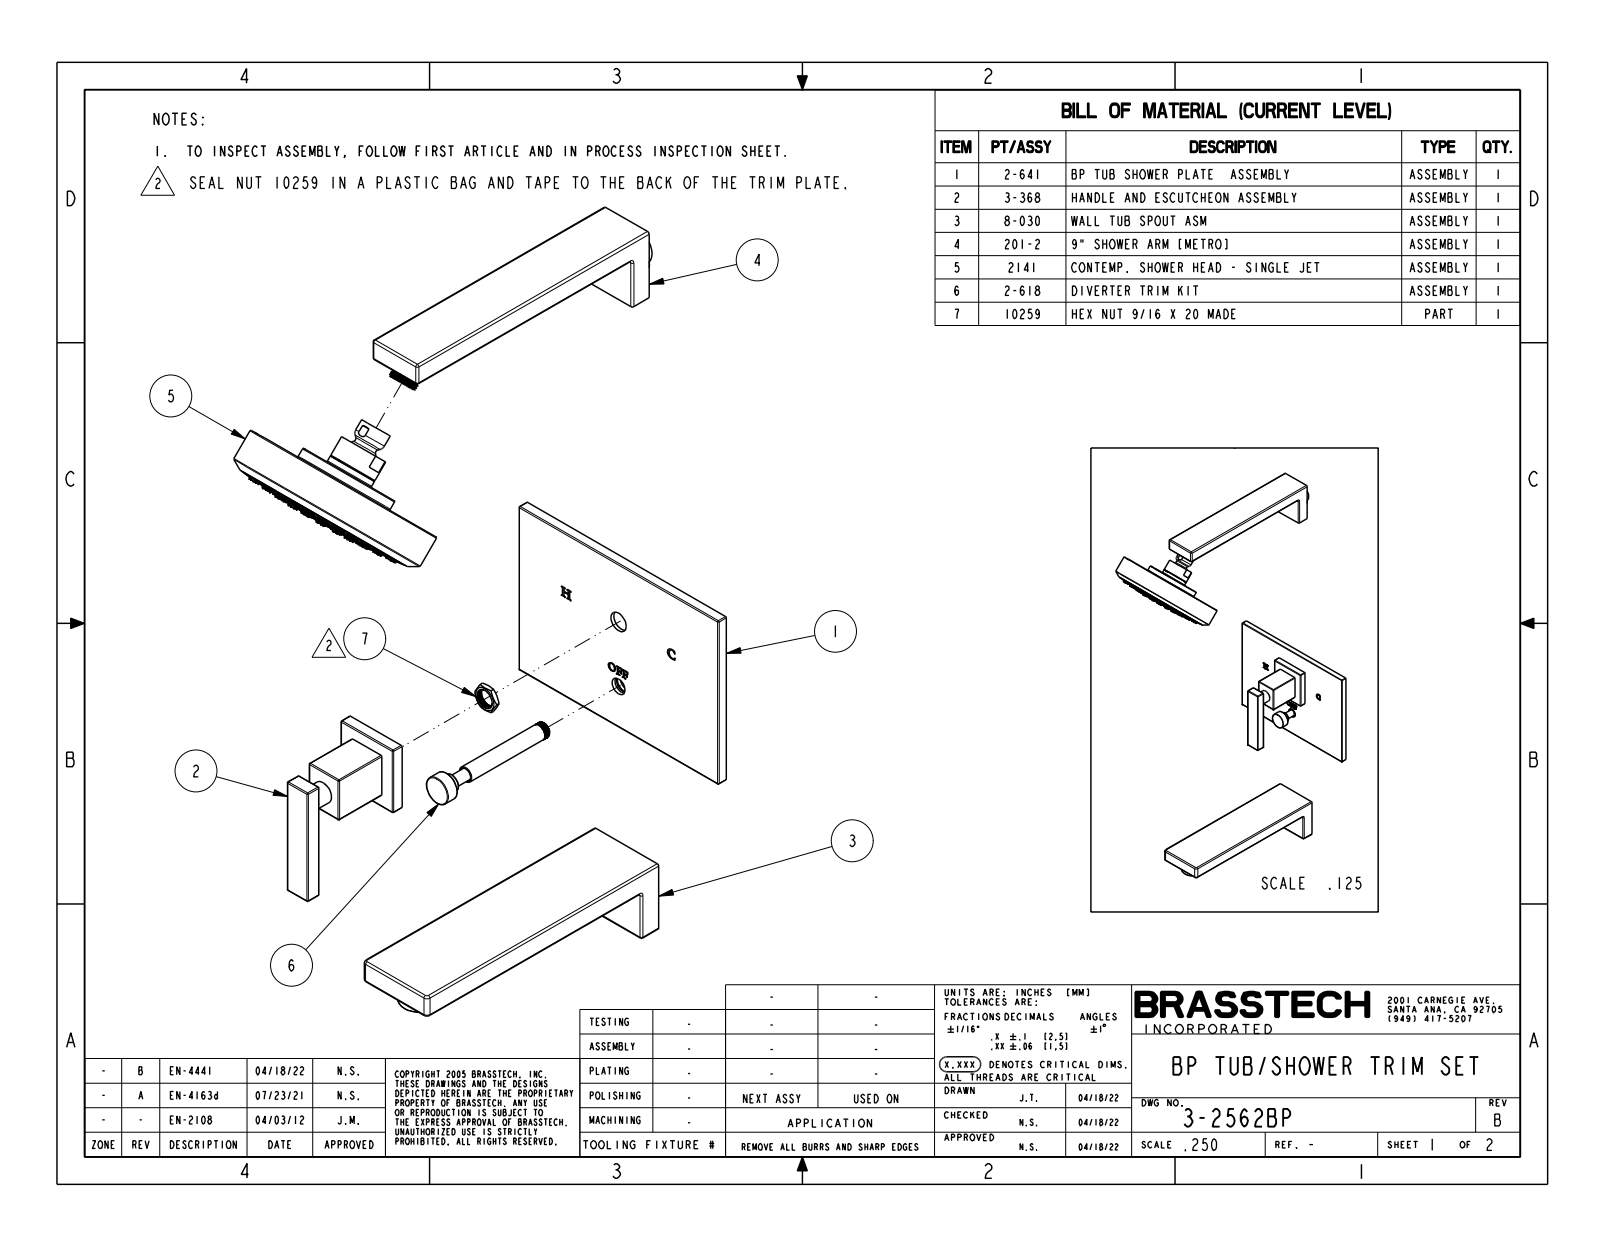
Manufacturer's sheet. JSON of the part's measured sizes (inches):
{"part_name": "3-2562BP", "step_written_by": "CREO PARAMETRIC BY PTC INC, 2018400 (AUTOMOTIVE_DESIGN)", "units": "inches", "bodies": {"solids": 67, "faces": 2097, "planar": 476, "cylindrical": 890, "other": 731}, "overall_size": [23.3, 12.907, 7.75], "volume_in3": 55.29, "surface_area_in2": 460.5, "round_holes": [[0.05, 90], [0.125, 90], [0.155, 1], [0.22, 1], [0.394, 1], [0.5, 1], [0.526, 1], [0.59, 1], [0.6, 1], [0.604, 1], [0.917, 1], [0.922, 1]], "round_bosses_or_shafts": [[0.198, 90], [1.4, 2], [5.91, 1], [5.22, 1], [5.1, 1], [2.92, 1], [1.8, 1], [1.75, 1]], "partial_cylinders_radius": [[0.03, 36], [0.125, 24], [0.06, 21], [0.532, 4], [0.08, 2], [0.118, 2], [0.475, 1], [1.4, 1]], "face_to_face_distances": [0.11, 0.67, 0.06, 0.796, 0.1, 0.896, 0.837, 0.737, 21.1, 0.654], "hole_center_spacings": [1.84, 1.84, 2.27, 0.48, 0.952, 1.408, 3.187, 3.555]}
